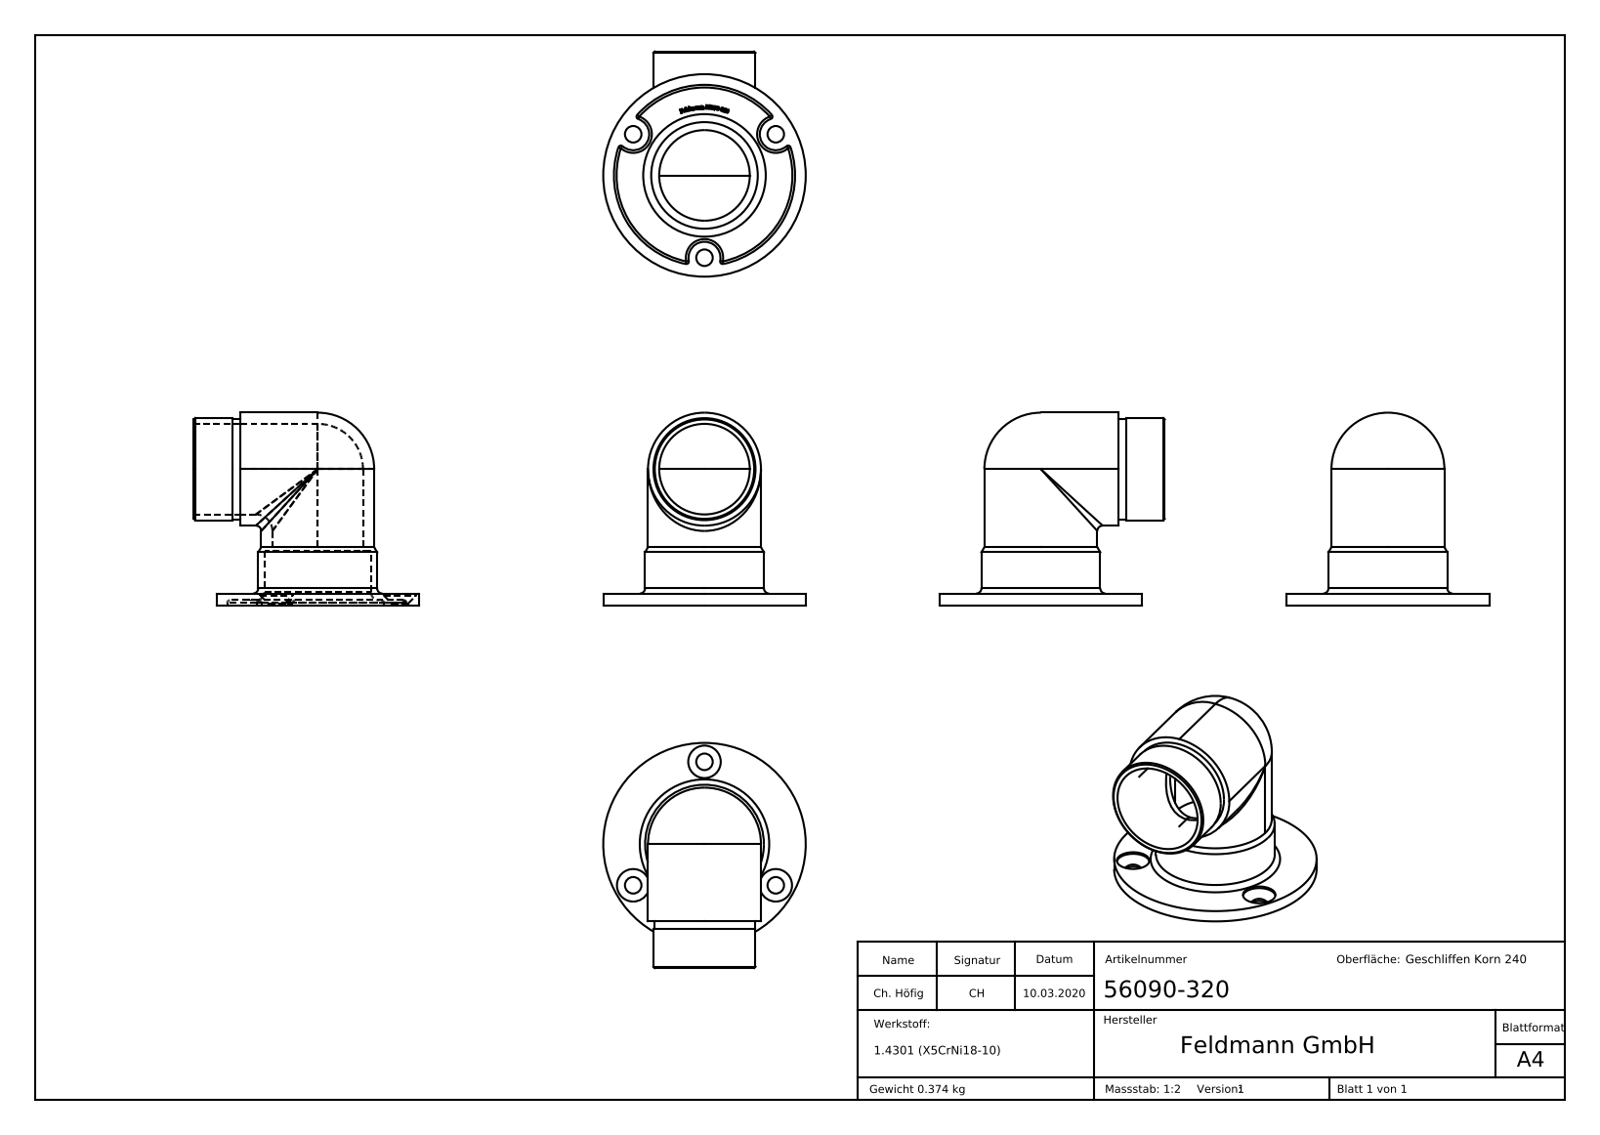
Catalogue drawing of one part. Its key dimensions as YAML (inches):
part_name: "56090-320"
step_written_by: "SolidWorks 2015 (CONFIG_CONTROL_DESIGN)"
units: inches
bodies: {solids: 1, faces: 295, planar: 111, cylindrical: 36, other: 148}
overall_size: [3.327, 2.992, 2.85]
volume: 2.887
surface_area: 47.39
round_holes:
  - {diameter: 0.244, count: 3}
  - {diameter: 0.48, count: 3}
  - {diameter: 1.339, count: 2}
  - {diameter: 1.575, count: 1}
  - {diameter: 2.677, count: 1}
round_bosses_or_shafts:
  - {diameter: 1.669, count: 2}
  - {diameter: 2.992, count: 1}
  - {diameter: 1.756, count: 1}
  - {diameter: 1.508, count: 1}
  - {diameter: 1.492, count: 1}
partial_cylinders:
  - {radius: 0.039, count: 6}
  - {radius: 0.236, count: 3}
face_to_face_distances: [0.098, 0.079, 0.177, 0.807, 0.728, 0.63, 0.689, 0.118, 0.571, 0.083]
hole_center_spacings: [1.217, 2.107]
